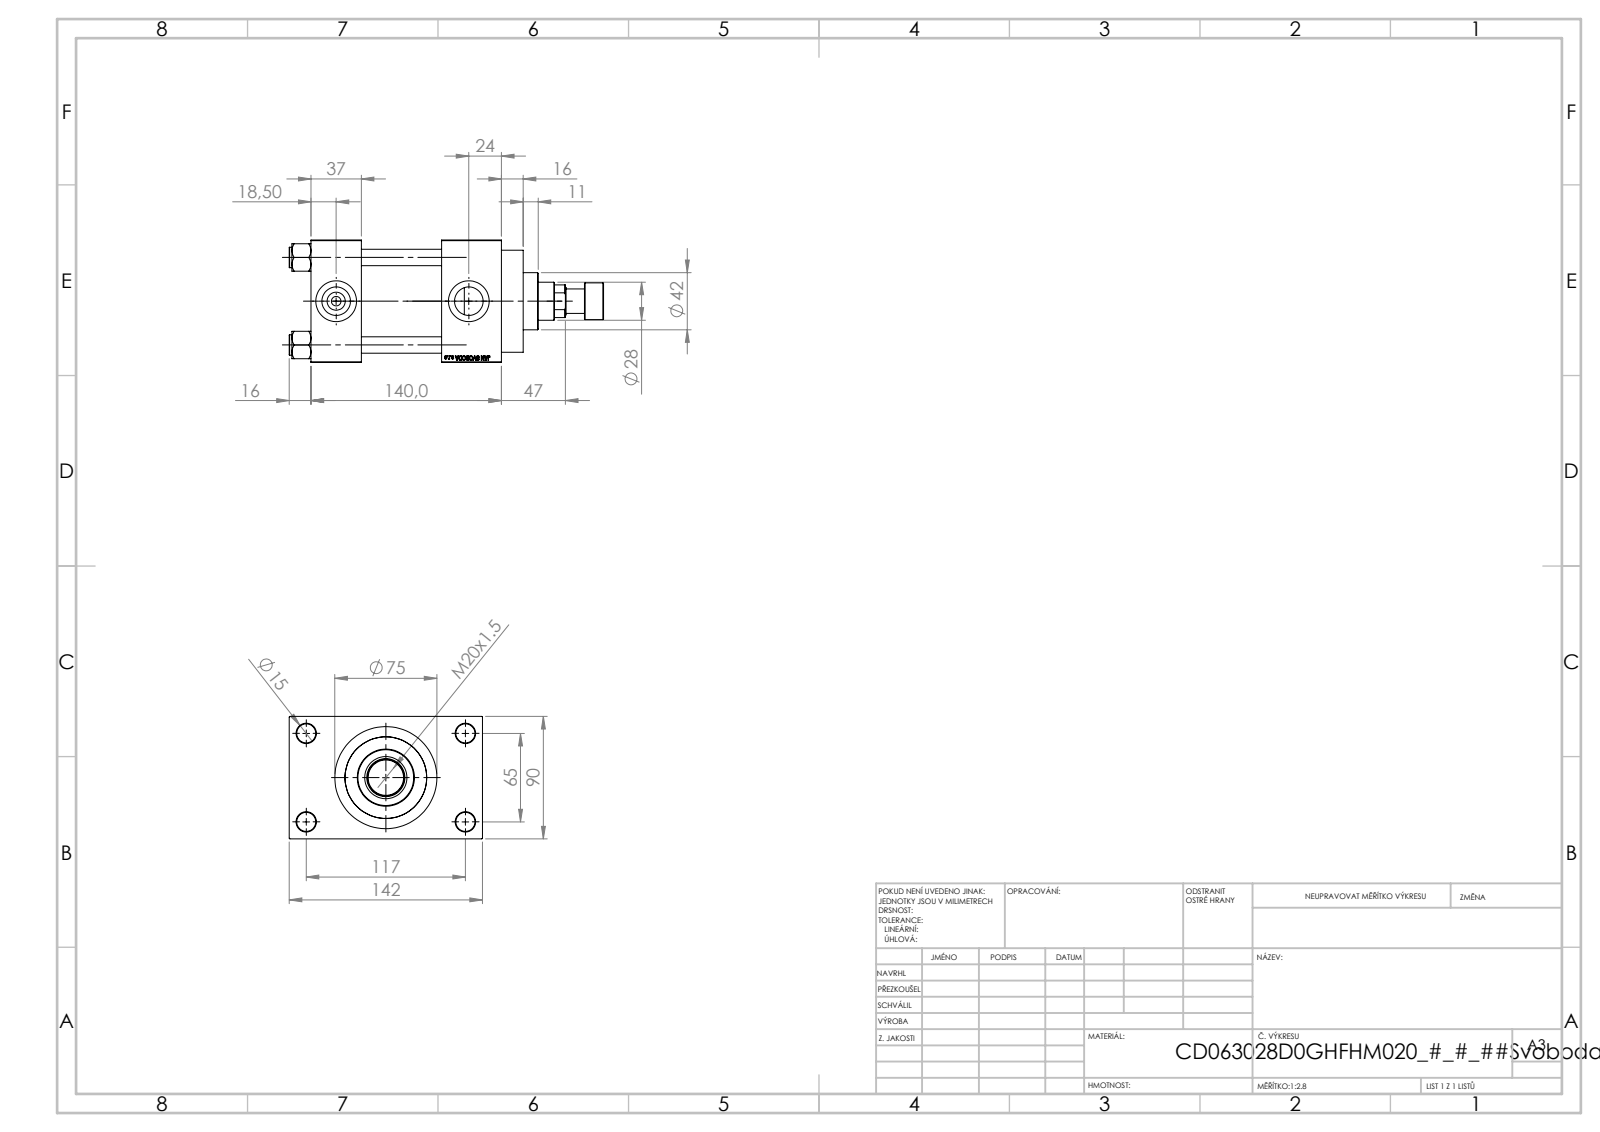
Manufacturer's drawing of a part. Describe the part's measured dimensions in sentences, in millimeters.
The part is named "V215CD_NUT_M5_D; V215CR_ROD_END_F; V215CD_D_TYCINKA; V215CD_VCP_D (+2 more)". Its 3-D file was written by "SolidWorks 2019 (CONFIG_CONTROL_DESIGN)". It is 12 solids with 1117 faces: 501 planar, 92 cylindrical and 524 other. Overall it measures 231 by 142 by 90 millimeters. Its volume is 1 108 000 cubic millimeters and its surface area 203 570 square millimeters. Round holes: 4 of diameter 12, 4 of diameter 14, 2 of diameter 7, 2 of diameter 20.96, 2 of diameter 30, 1 of diameter 18.5, 1 of diameter 28, 1 of diameter 31, 1 of diameter 50, 1 of diameter 60, 1 of diameter 63. Round bosses or shafts: 4 of diameter 15, 1 of diameter 75, 1 of diameter 69, 1 of diameter 42, 1 of diameter 27, 1 of diameter 18. The main face-to-face distances are 90, 59, 37, 96, 140, 103, 44, 26, 116, 119. The hole center spacings are 26.35, 45.47, 64.3, 66.92, 69.81, 90.65, 111.34, 65.
